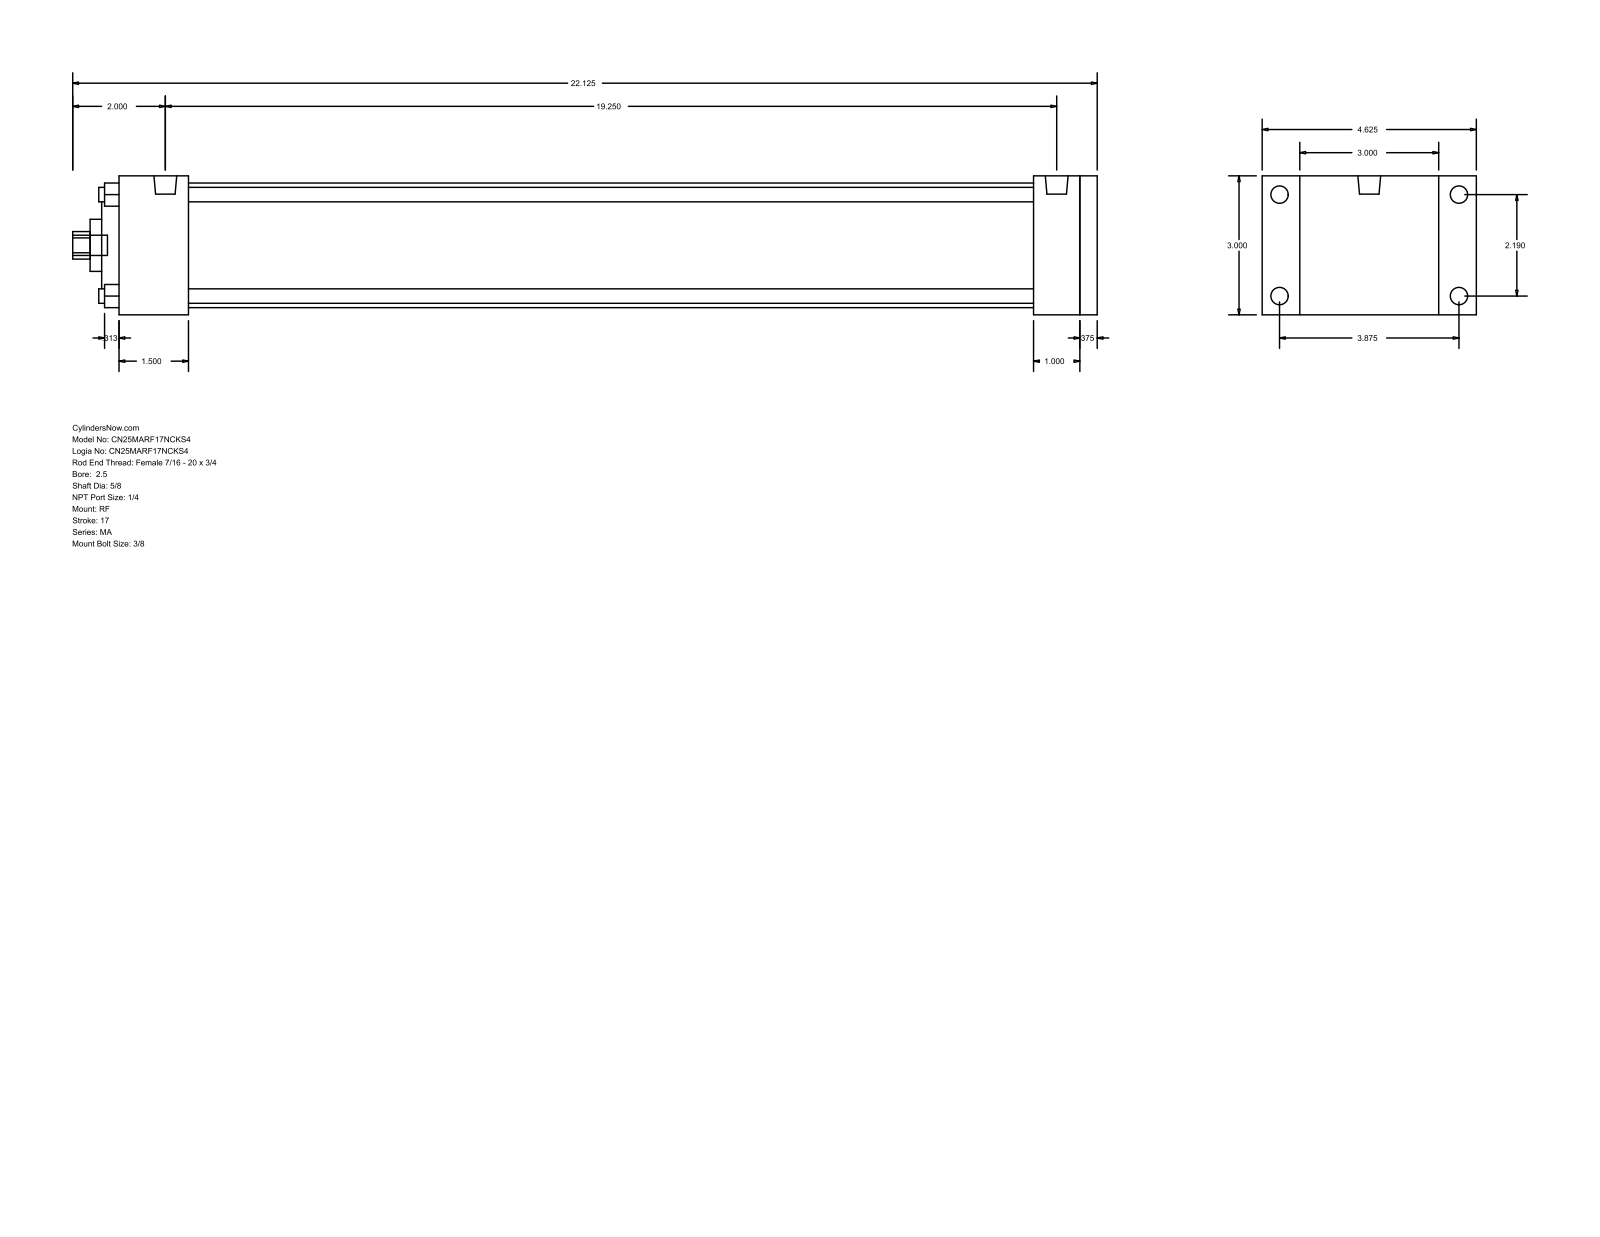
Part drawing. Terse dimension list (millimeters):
name: MA_RF__0250_0.625
written by: GSSL Pune (CONFIG_CONTROL_DESIGN)
unit: mm
bodies: 0 solids, 94 faces (65 planar, 29 cylindrical, 0 other)
size: 561.98 × 117.47 × 76.2
holes: 4× ⌀7.94, 1× ⌀15.88, 1× ⌀28.57, 1× ⌀50.8, 1× ⌀68.33
bosses: 4× ⌀9.53, 4× ⌀7.94, 2× ⌀12.49, 1× ⌀11.11
rounds: 1× R7.54
face distances: 76.2, 536.58, 9.53, 527.05, 25.4, 38.1, 501.65, 463.55, 488.95, 498.48
hole spacings: 39.33, 55.62, 78.66
